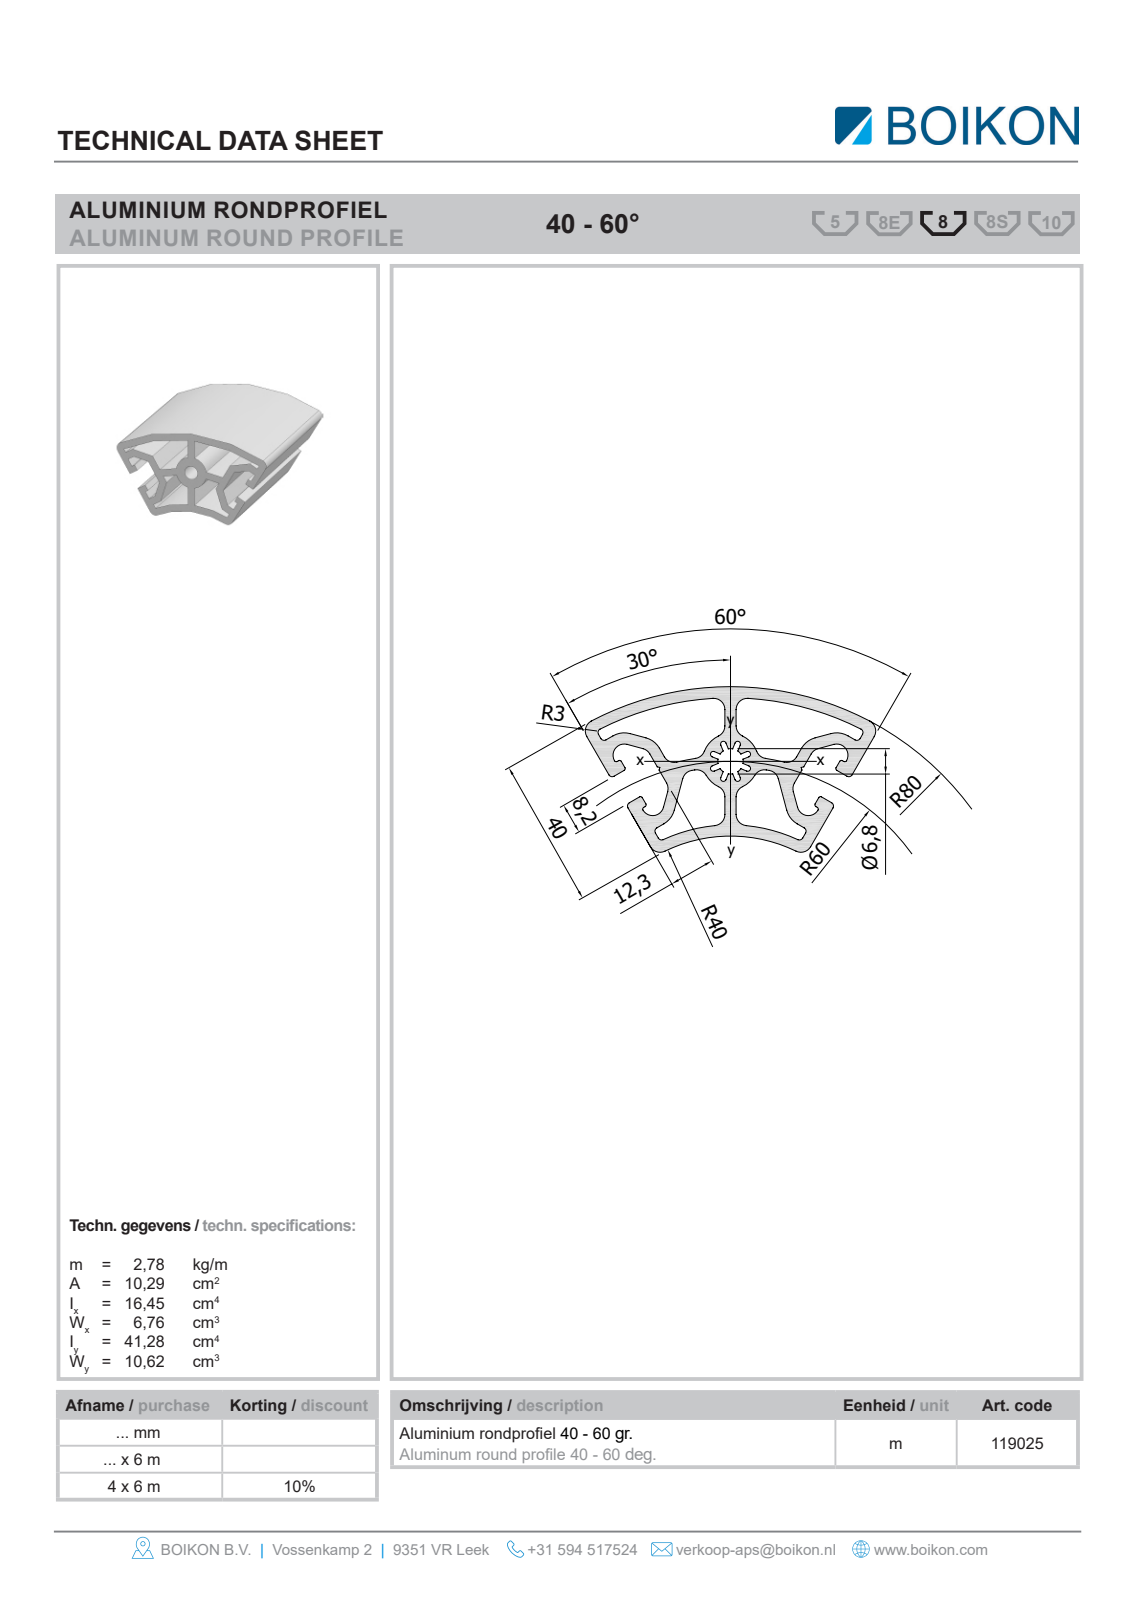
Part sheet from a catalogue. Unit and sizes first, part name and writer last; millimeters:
Units: millimetres
Overall size (bounding box): 1000 × 68.13 × 58.9
Round holes (diameter × count): ⌀6.8 ×1
Partial cylindrical surfaces — rounded edges, fillets, slot ends (radius × count): R3 ×4, R7.9 ×1, R40 ×1, R43.5 ×1, R58.25 ×1, R61.75 ×1, R76.5 ×1, R80 ×1
Main face-to-face distances: 3.5, 12.1, 2.9, 15.6, 11.1, 10.4, 18.6, 9.2, 12.7, 25.5
Volume: 1 153 000 mm³ · Surface area: 624 686 mm²
Bodies: 1 solid, 71 faces (52 planar, 19 cylindrical, 0 other)
Part name (STEP PRODUCT): Root; 119025Rondprofiel 40-60gr.BOIKON0
STEP written by: HiCAD 2013 1802.4 Build 509 (AUTOMOTIVE_DESIGN)
